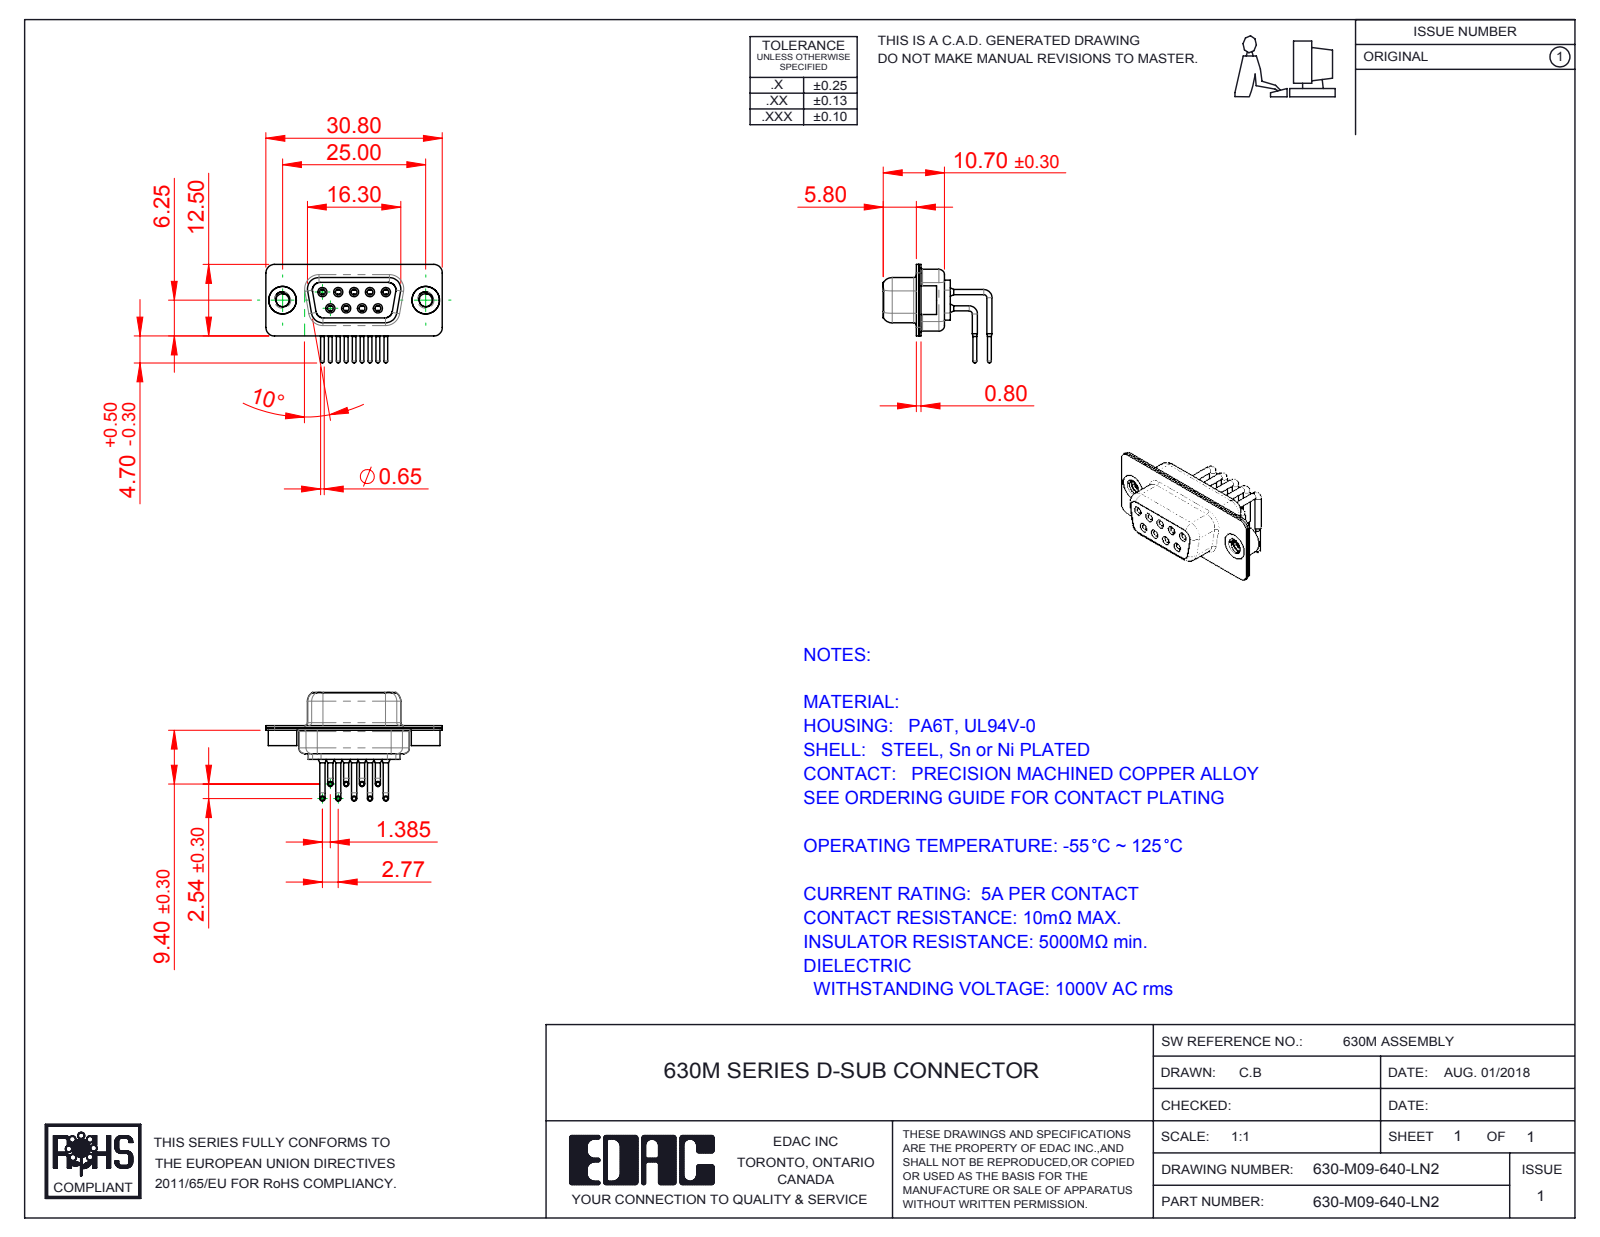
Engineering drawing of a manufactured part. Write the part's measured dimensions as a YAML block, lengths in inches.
part_name: "630M Shell Rear_09 Contacts; 630-M09-640-LN2; 630M Shell Front_09 Contacts; 630M Housing_09 Contacts (+3 more)"
step_written_by: "SolidWorks 2016 (CONFIG_CONTROL_DESIGN)"
units: inches
bodies: {solids: 14, faces: 756, planar: 202, cylindrical: 344, other: 210}
overall_size: [1.213, 0.748, 0.677]
volume: 0.107
surface_area: 7.192
round_holes:
  - {diameter: 0.039, count: 9}
  - {diameter: 0.043, count: 9}
  - {diameter: 0.067, count: 9}
  - {diameter: 0.071, count: 9}
  - {diameter: 0.079, count: 9}
  - {diameter: 0.089, count: 2}
  - {diameter: 0.157, count: 2}
  - {diameter: 0.189, count: 2}
round_bosses_or_shafts:
  - {diameter: 0.035, count: 18}
  - {diameter: 0.063, count: 9}
  - {diameter: 0.059, count: 9}
  - {diameter: 0.026, count: 9}
  - {diameter: 0.197, count: 2}
  - {diameter: 0.193, count: 2}
partial_cylinders:
  - {radius: 0.059, count: 16}
  - {radius: 0.079, count: 12}
  - {radius: 0.053, count: 8}
  - {radius: 0.063, count: 8}
  - {radius: 0.01, count: 4}
  - {radius: 0.02, count: 4}
  - {radius: 0.024, count: 4}
  - {radius: 0.026, count: 4}
face_to_face_distances: [0.016, 0.031, 0.057, 0.091, 0.352, 0.244, 0.335, 0.075, 0.033, 0.368]
hole_center_spacings: [0.124, 0.109, 0.218, 0.198, 0.198, 0.327, 0.28, 0.294]
